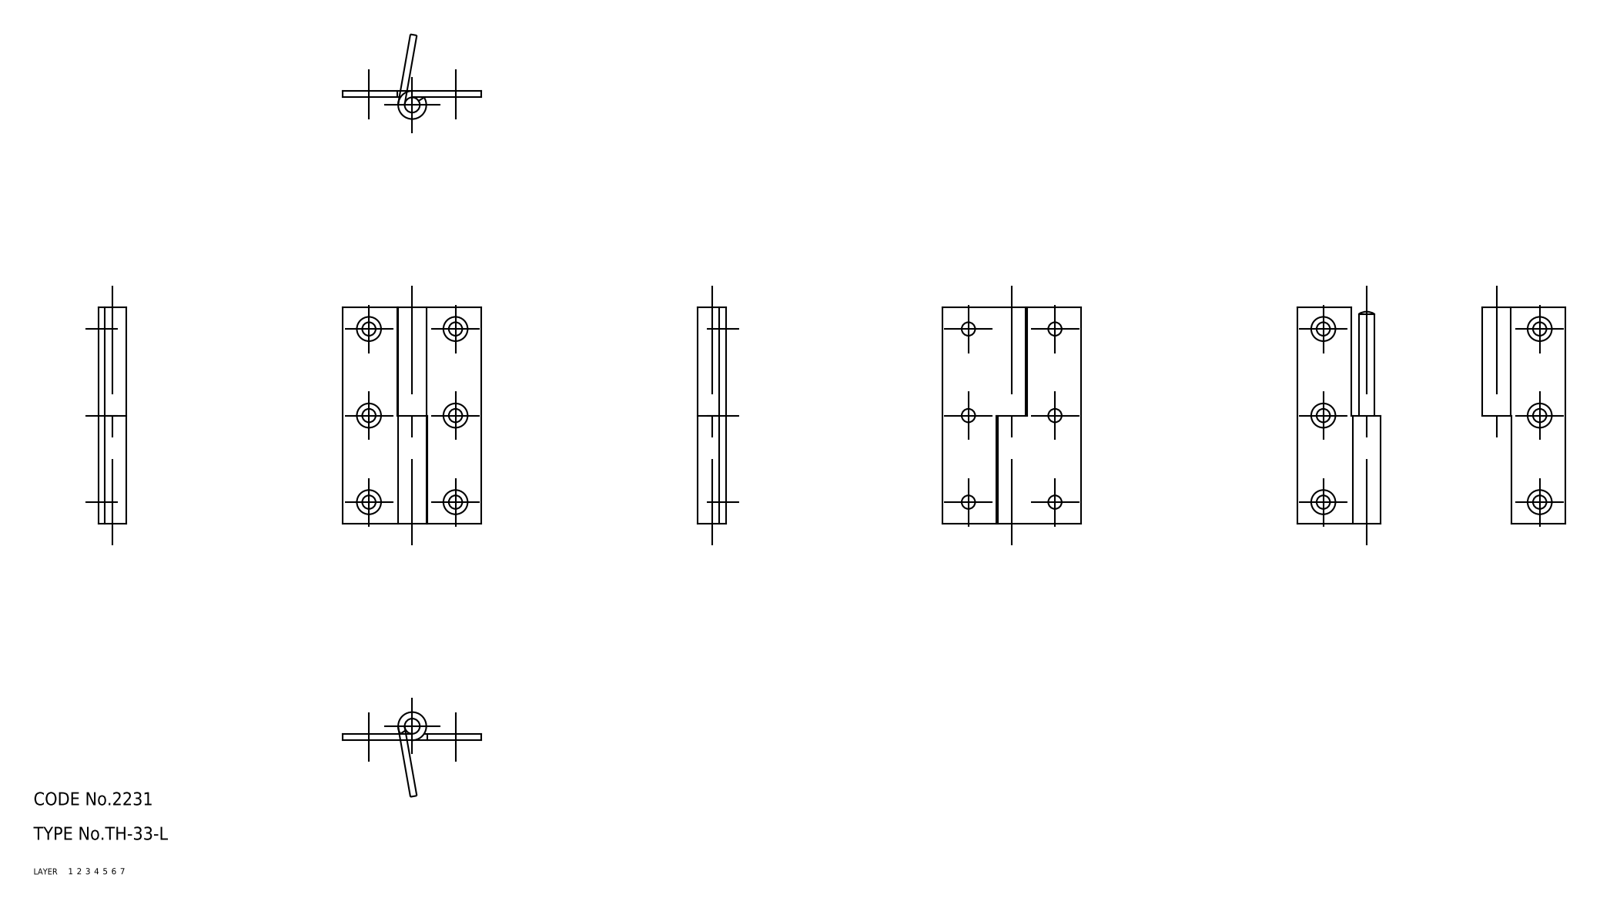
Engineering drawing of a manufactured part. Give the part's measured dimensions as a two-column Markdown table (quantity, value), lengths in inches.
| quantity | value |
| --- | --- |
| part name | shaft; hinge piece_B; hinge piece_A; TH_33_L_8072_36 |
| STEP written by | CADfix (AUTOMOTIVE_DESIGN) |
| units | inches |
| bodies | 3 solids, 48 faces (0 planar, 0 cylindrical, 48 other) |
| overall size | 1.969 × 1.26 × 0.256 |
| volume | 0.212 in³ |
| surface area | 8 in² |
